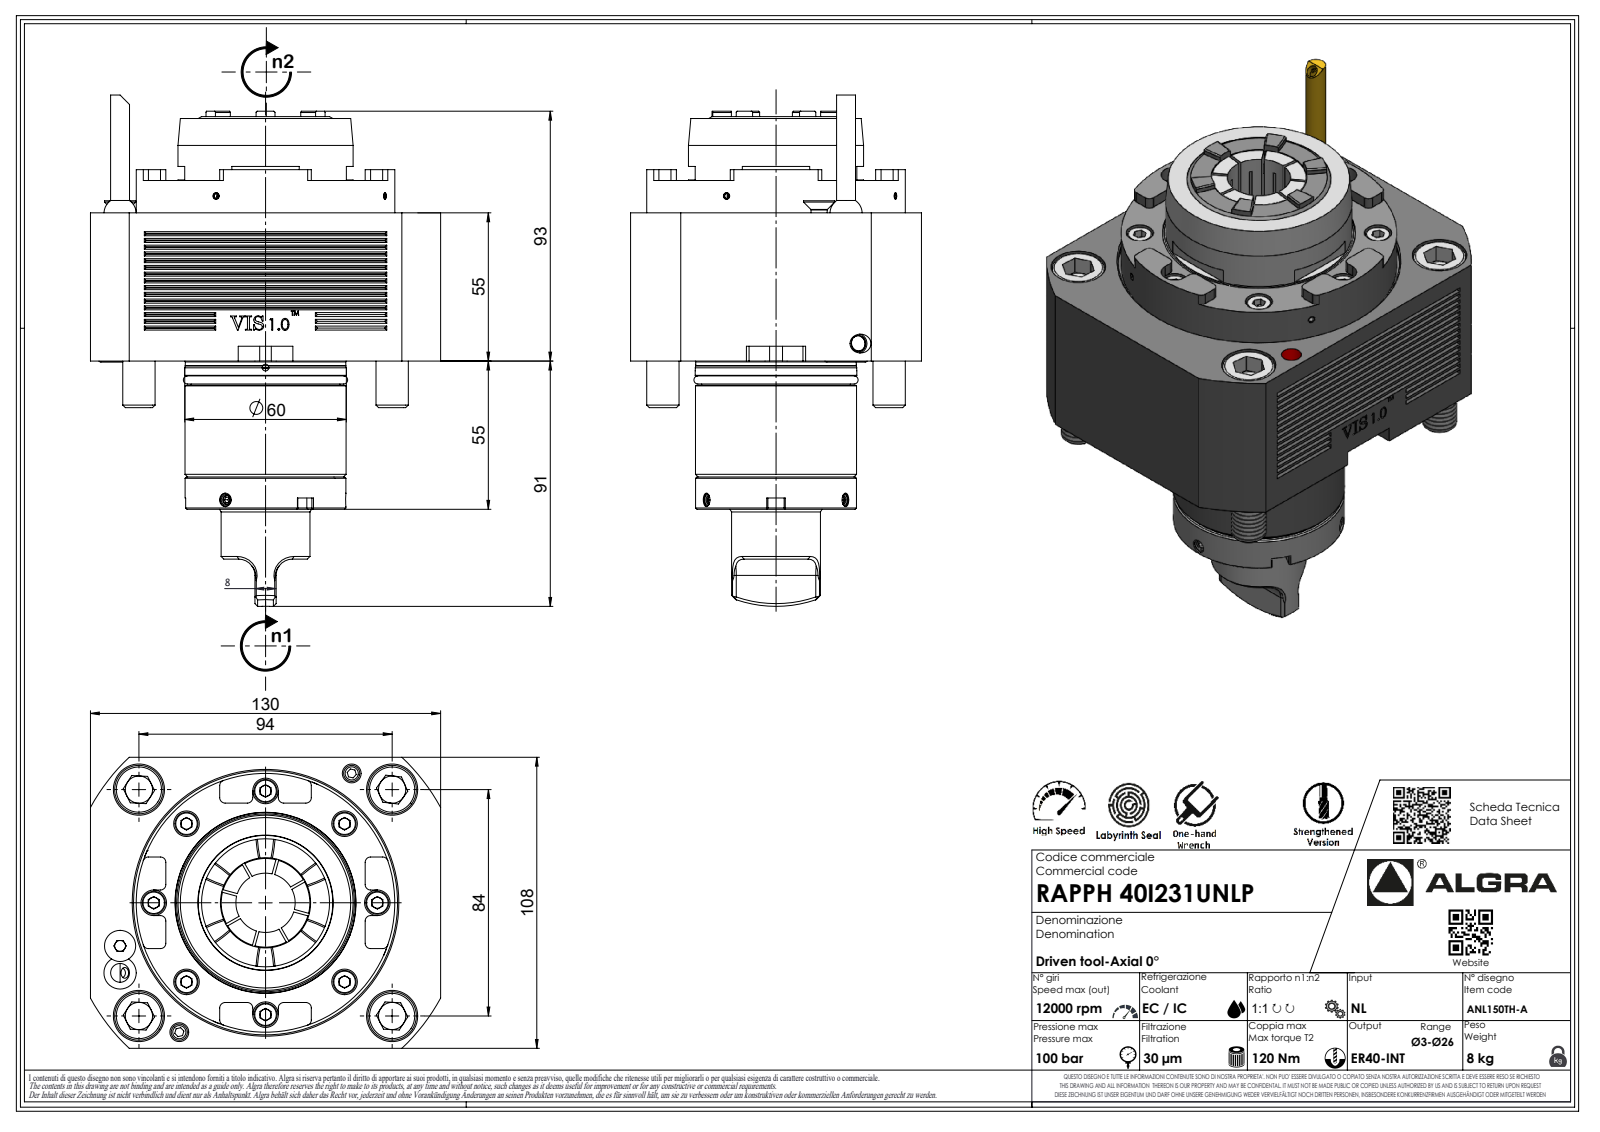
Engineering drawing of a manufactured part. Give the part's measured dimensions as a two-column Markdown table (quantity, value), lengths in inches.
| quantity | value |
| --- | --- |
| part name | RAPPH40I231UNLP |
| STEP written by | SolidWorks 2023 (AUTOMOTIVE_DESIGN) |
| units | inches |
| bodies | 1 solid, 559 faces (360 planar, 88 cylindrical, 111 other) |
| overall size | 7.126 × 5.118 × 4.252 |
| volume | 66.03 in³ |
| surface area | 123.3 in² |
| round holes (diameter × count) | 0.374 × 4, 0.083 × 1 |
| round bosses / shafts (diameter × count) | 0.472 × 4, 3.78 × 1, 2.559 × 1, 2.362 × 1, 2.354 × 1, 2.35 × 1, 2.346 × 1, 2.173 × 1 |
| partial cylindrical surfaces (radius × count) | 0.079 × 24, 0.315 × 8, 0.013 × 7, 0.02 × 7, 0.146 × 7, 0.236 × 6, 0.118 × 3, 0.008 × 1 |
| main face-to-face distances | 2.165, 4.252, 5.118, 1.378, 2.638, 3.543, 0.472, 0.906, 0.217, 1.949 |
| hole center spacings | 2.311, 3.268 |
